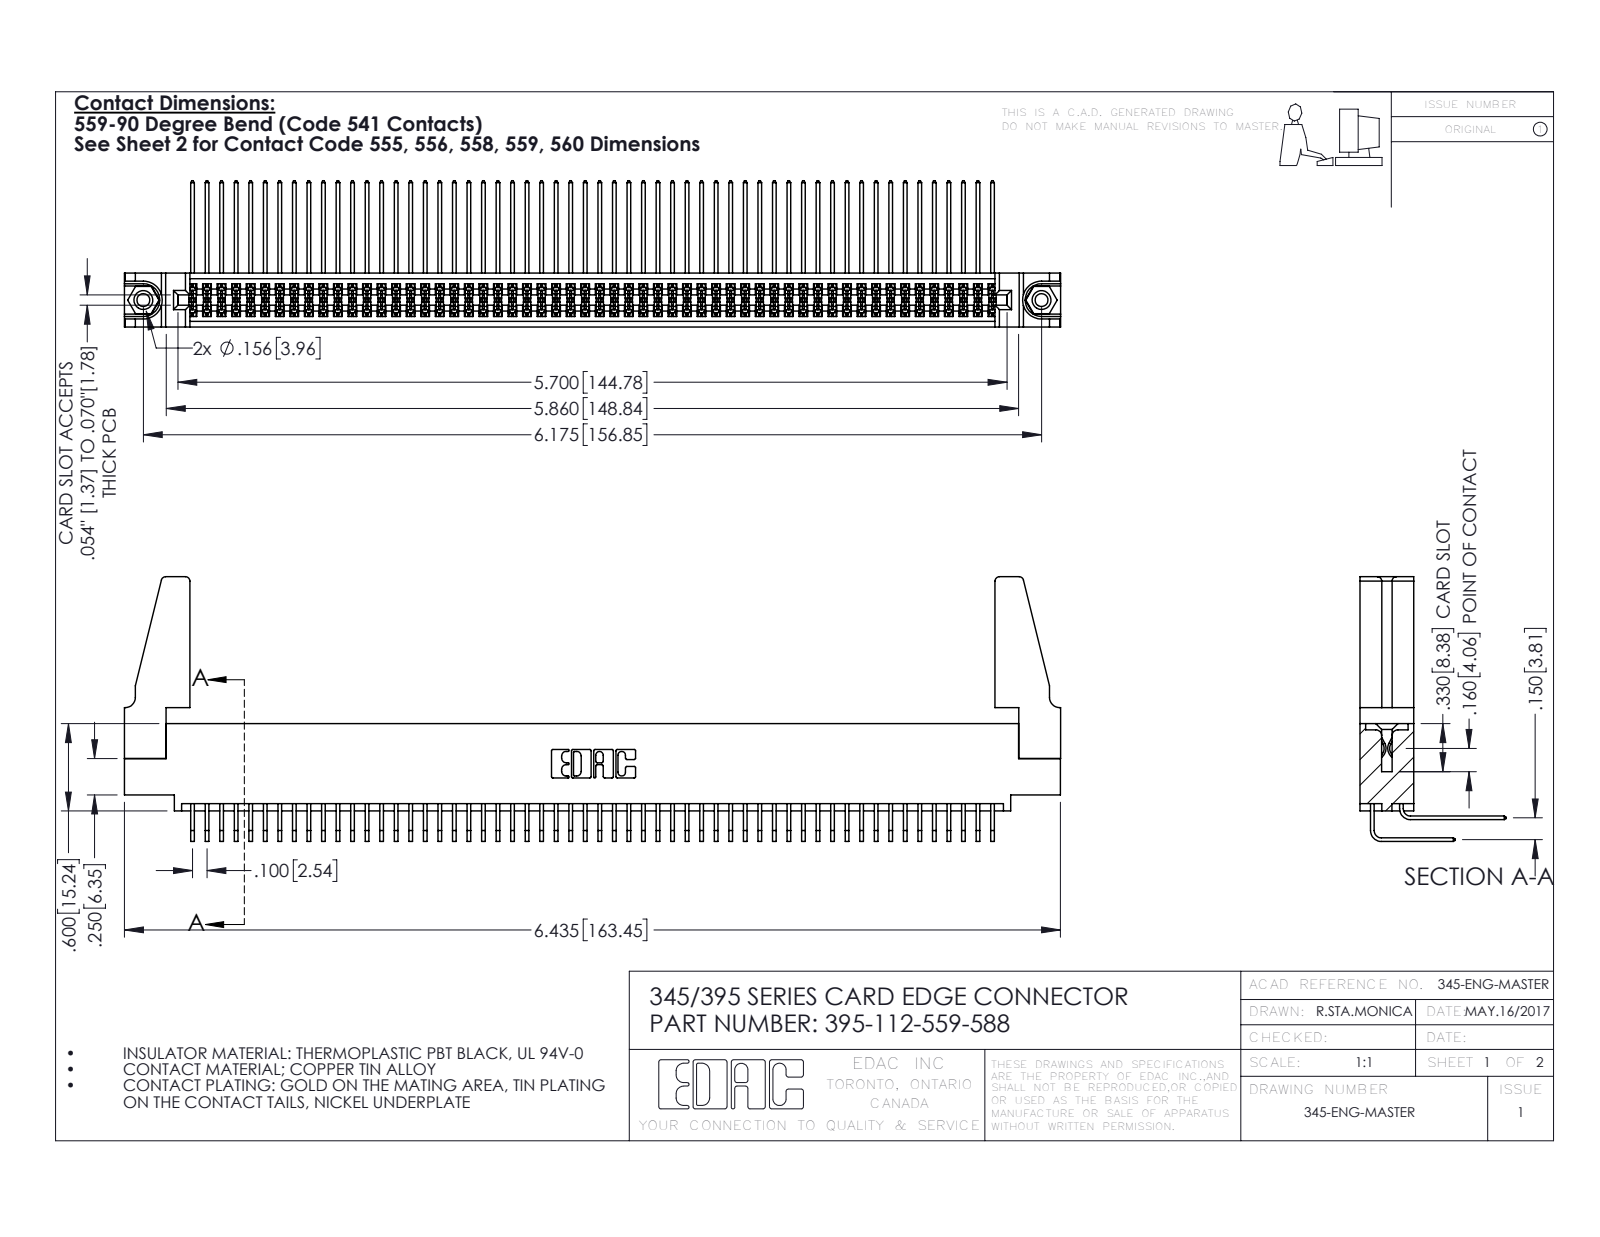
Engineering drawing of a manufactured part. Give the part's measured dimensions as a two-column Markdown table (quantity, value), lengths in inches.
| quantity | value |
| --- | --- |
| part name | 395-112-559-588; 345-250-001_345-250-001-102; 345 Part_0.110 Offset - 0.156 Dia-TH; 345-292-001_558 559 Tail - 1 (+2 more) |
| STEP written by | SolidWorks 2016 (CONFIG_CONTROL_DESIGN) |
| units | inches |
| bodies | 117 solids, 6078 faces (4076 planar, 1986 cylindrical, 16 other) |
| overall size | 6.436 × 1.819 × 1.005 |
| volume | 1.21 in³ |
| surface area | 48.11 in² |
| round holes (diameter × count) | 0.089 × 2, 0.125 × 2, 0.156 × 2, 0.064 × 1 |
| round bosses / shafts (diameter × count) | 0.155 × 2 |
| partial cylindrical surfaces (radius × count) | 0.006 × 168, 0.01 × 22, 0.03 × 8, 0.007 × 6, 0.031 × 6, 0.026 × 3, 0.014 × 2, 0.019 × 2 |
| main face-to-face distances | 0.072, 0.298, 0.37, 0.2, 0.098, 0.272, 0.025, 0.225, 0.175, 0.15 |
| hole center spacings | 0.27, 5.939, 6.175 |
